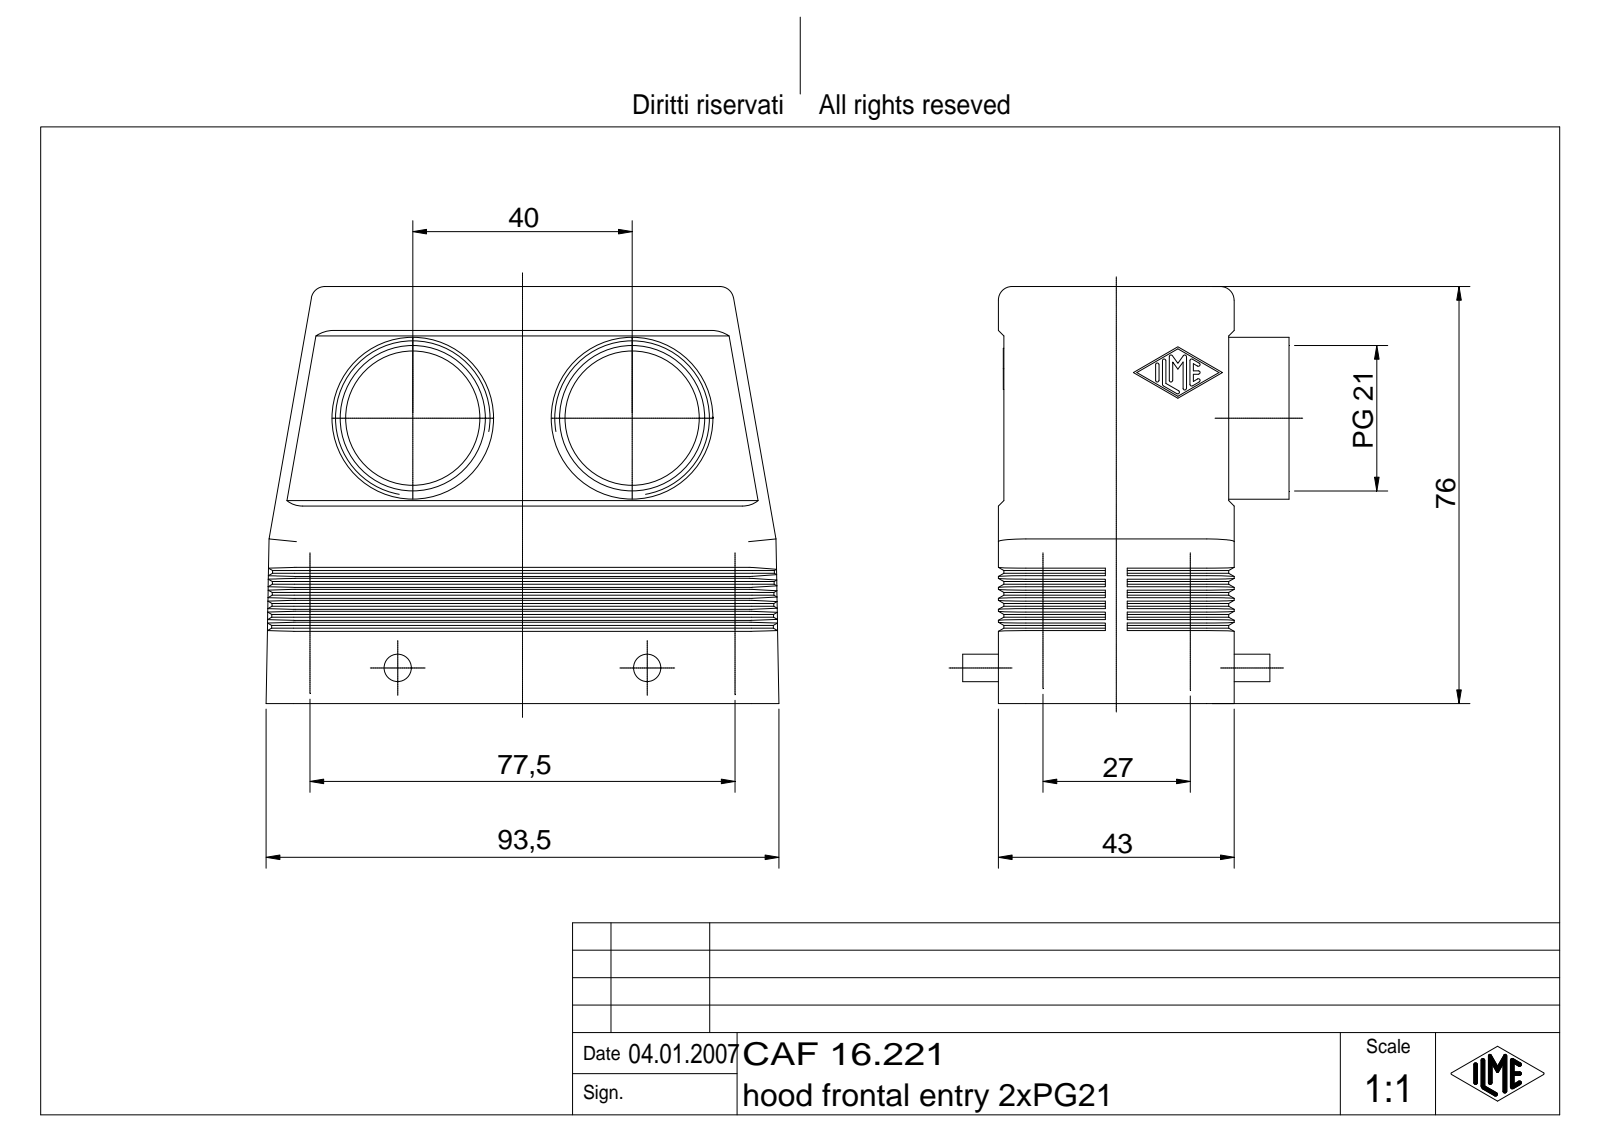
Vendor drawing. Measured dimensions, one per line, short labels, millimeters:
name: CAF 16.221
written by: Autodesk Inventor 7 (AUTOMOTIVE_DESIGN)
unit: mm
bodies: 1 solid, 456 faces (150 planar, 136 cylindrical, 170 other)
size: 93.5 × 76 × 59.5
volume: 68 596 mm³; area: 48 132 mm²
holes: 2× ⌀24.5, 1× ⌀26.5, 1× ⌀28
bosses: 2× ⌀5, 1× ⌀29.5
rounds: 14× R0.25, 12× R4, 8× R2, 8× R5, 4× R2.5, 4× R3.5
face distances: 3, 40, 37, 2, 39, 42, 1, 43, 41, 2.93
hole spacings: 40
